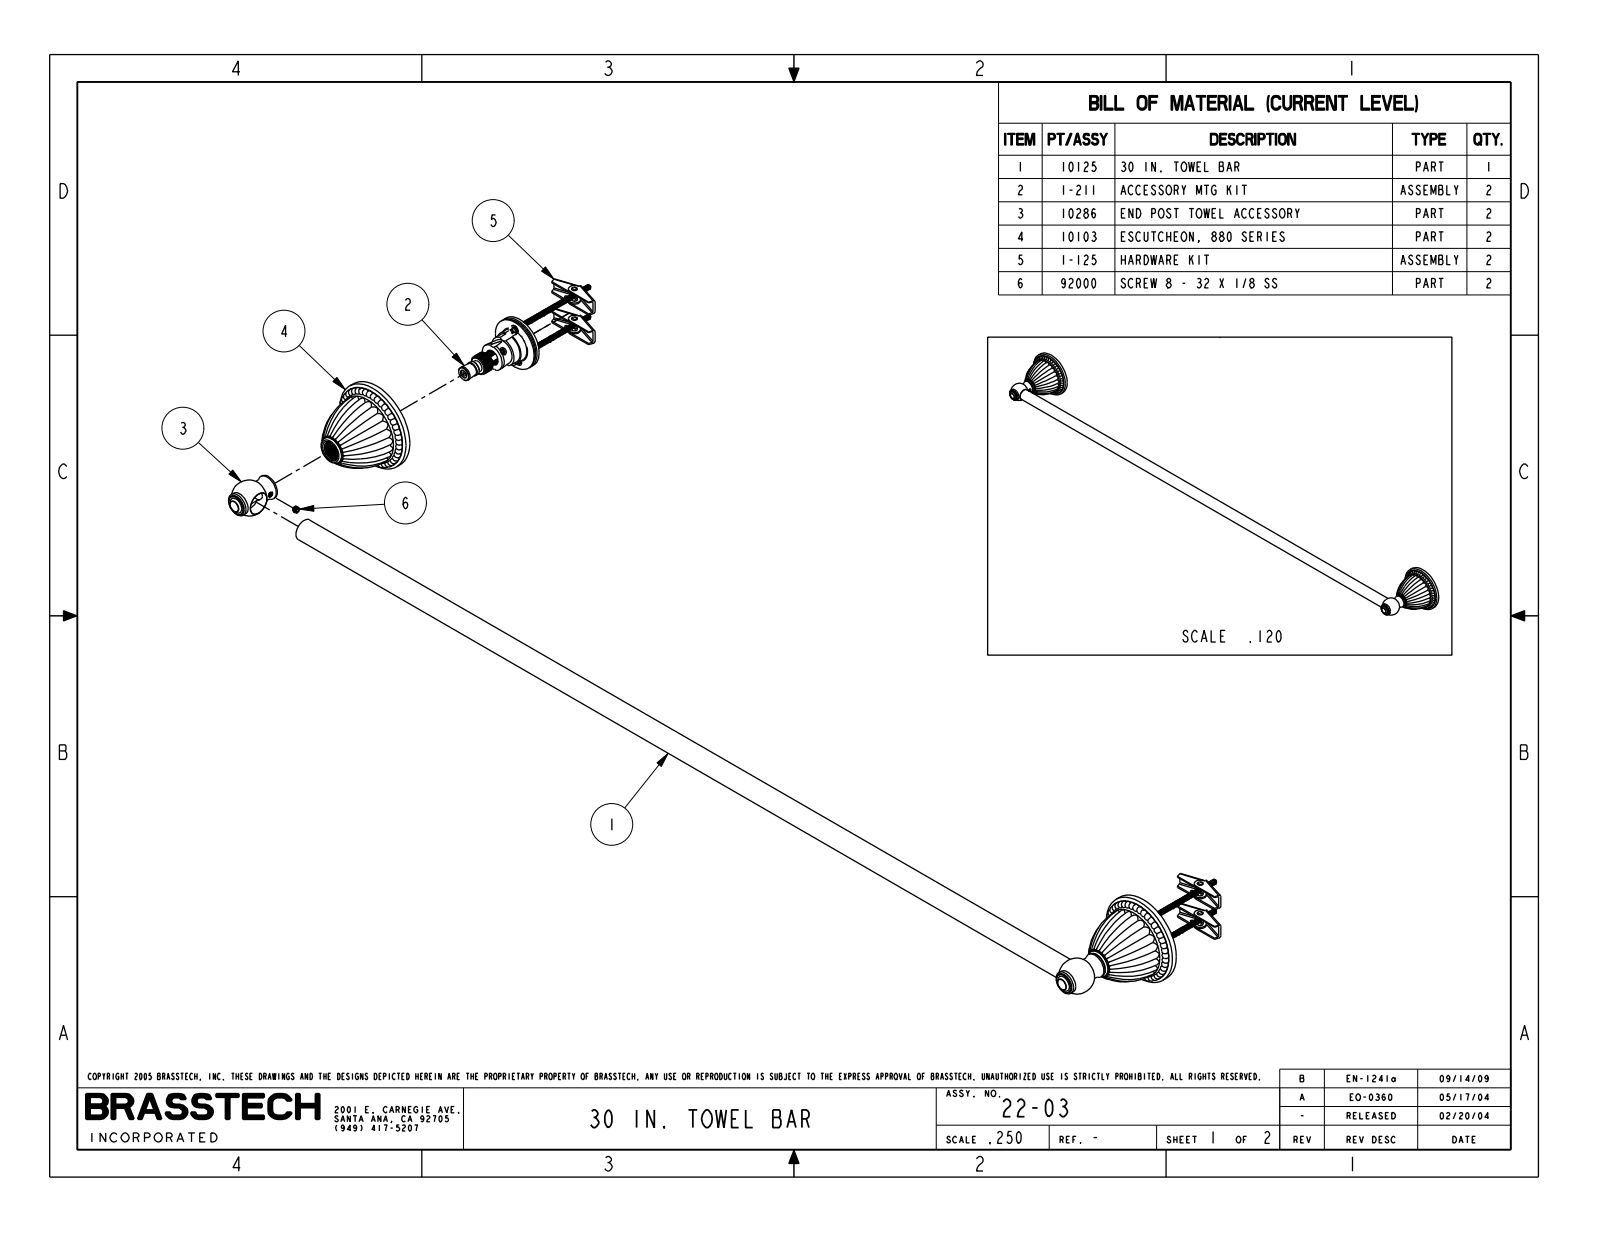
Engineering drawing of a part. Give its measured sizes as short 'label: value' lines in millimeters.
name: 22-03_WEB
written by: PRO/ENGINEER BY PARAMETRIC TECHNOLOGY CORPORATION, 2009300 (CONFIG_CONTROL_DESIGN)
unit: mm
bodies: 0 solids, 330 faces (60 planar, 18 cylindrical, 252 other)
size: 829.9 × 80.4 × 65.3
bosses: 2× ⌀65.3, 2× ⌀17.9, 2× ⌀16.8, 2× ⌀13.8, 1× ⌀15.9
face distances: 5.1, 78.1, 73, 78.7, 73.6, 0.6, 80.4, 75.3, 2.3, 1.7
